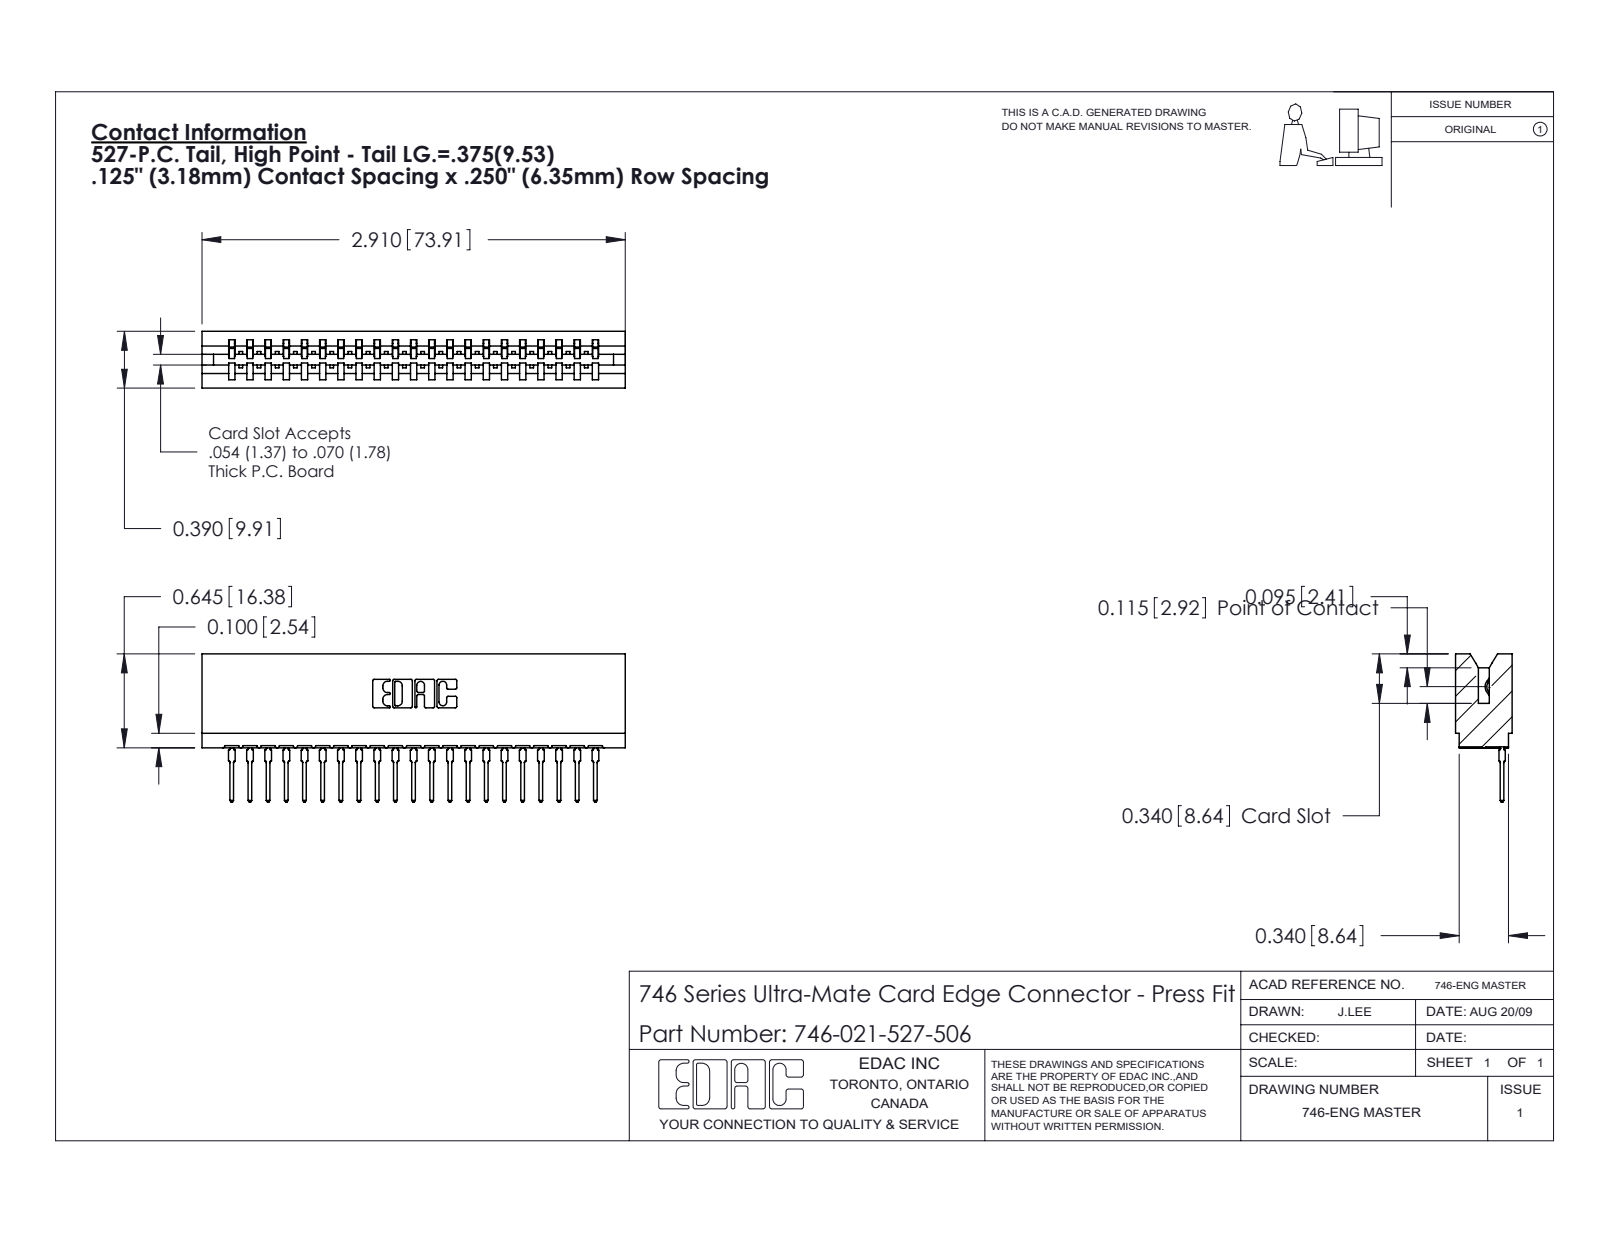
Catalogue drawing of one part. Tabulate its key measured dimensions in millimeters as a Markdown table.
| quantity | value |
| --- | --- |
| part name | 746-021-527-506; 746 Part_.340 Slot Depth - 06; 746-292-001_527 |
| STEP written by | SolidWorks 2020 (CONFIG_CONTROL_DESIGN) |
| units | millimeters |
| bodies | 22 solids, 2366 faces (1379 planar, 441 cylindrical, 546 other) |
| overall size | 73.9 × 25.9 × 9.9 |
| volume | 8 420 mm³ |
| surface area | 11 170 mm² |
| partial cylindrical surfaces (radius × count) | 0.5 × 42, 0.3 × 22, 0.4 × 22, 0.2 × 6, 0.8 × 6, 0.1 × 4, 0.3 × 4, 0.7 × 3 |
| main face-to-face distances | 8.5, 6.4, 1.4, 9.9, 12.7, 0.6, 7.8, 1.1, 3.2, 19.1 |
